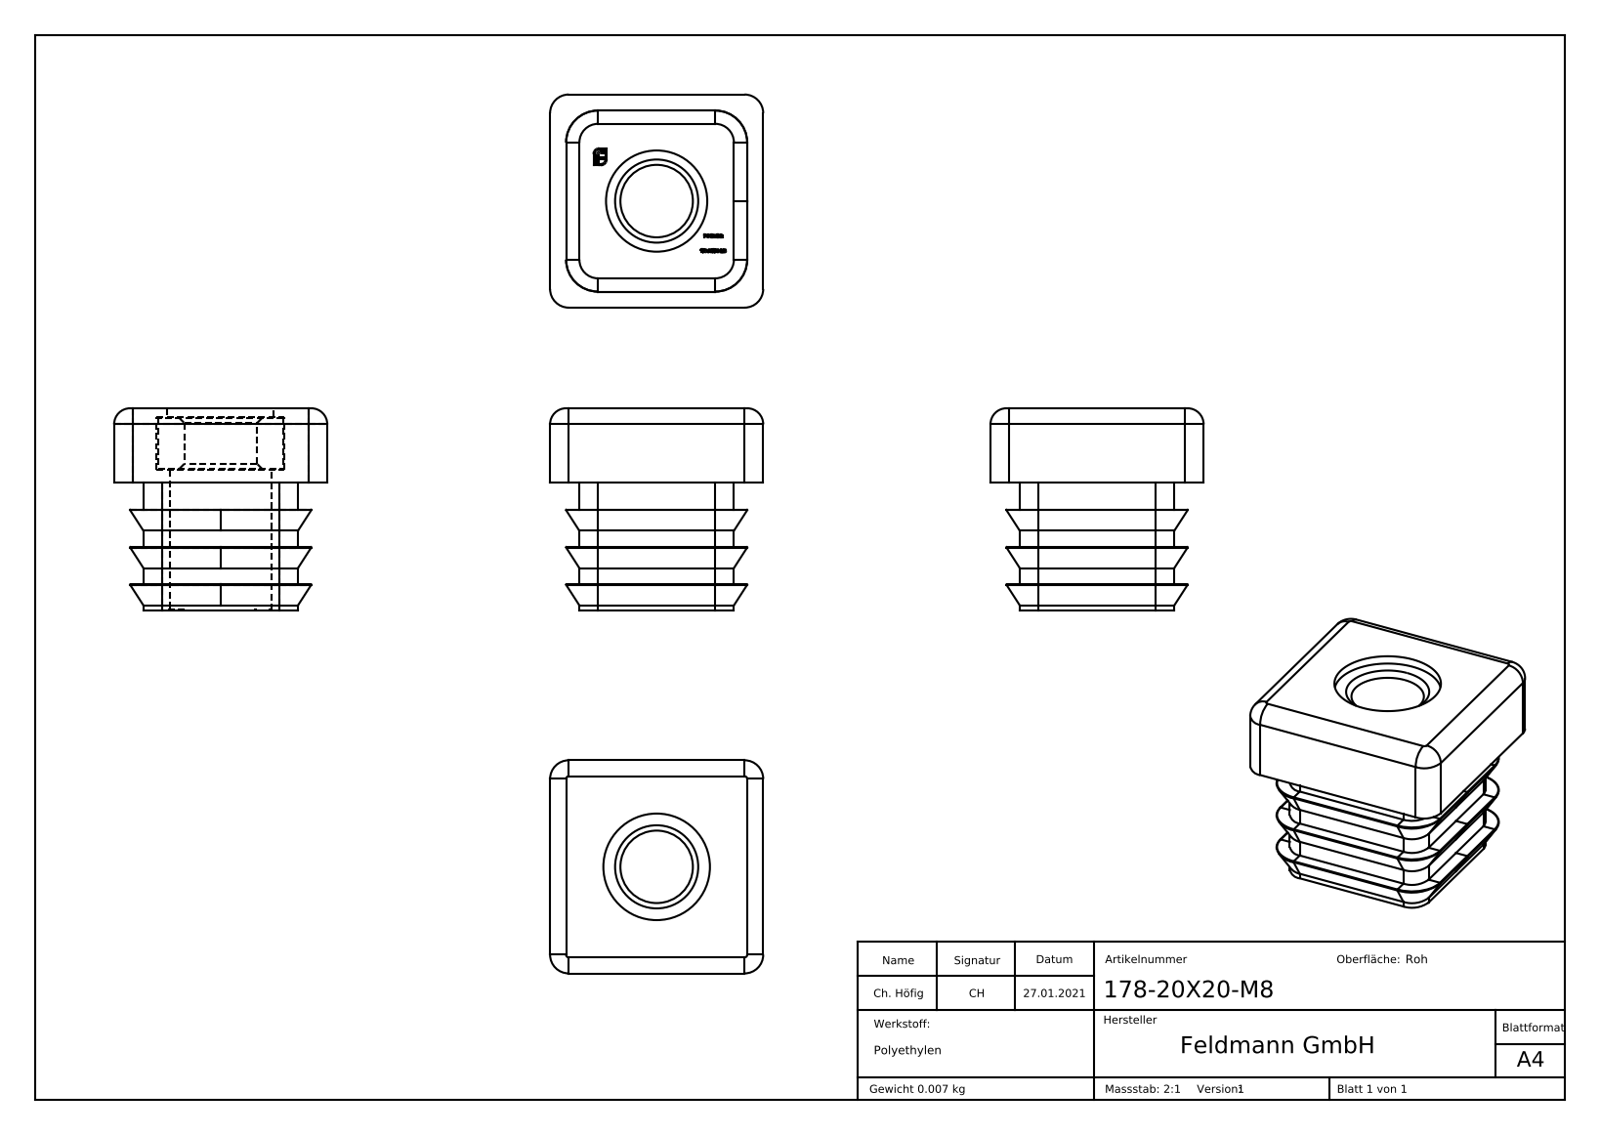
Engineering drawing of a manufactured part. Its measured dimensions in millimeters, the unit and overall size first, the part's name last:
Units: millimetres
Overall size (bounding box): 20 × 20 × 19
Round holes (diameter × count): ⌀6.8 ×1, ⌀9.5 ×1, ⌀10 ×1
Partial cylindrical surfaces — rounded edges, fillets, slot ends (radius × count): R1.75 ×8, R1.5 ×4
Main face-to-face distances: 2.75, 17.25, 7, 12, 4, 16, 1.25, 13.25, 11.9, 1.35
Volume: 4 230 mm³ · Surface area: 3 424 mm²
Bodies: 2 solids, 462 faces (238 planar, 60 cylindrical, 164 other)
Part name (STEP PRODUCT): 178-20X20-M8
STEP written by: SolidWorks 2018 (CONFIG_CONTROL_DESIGN)
